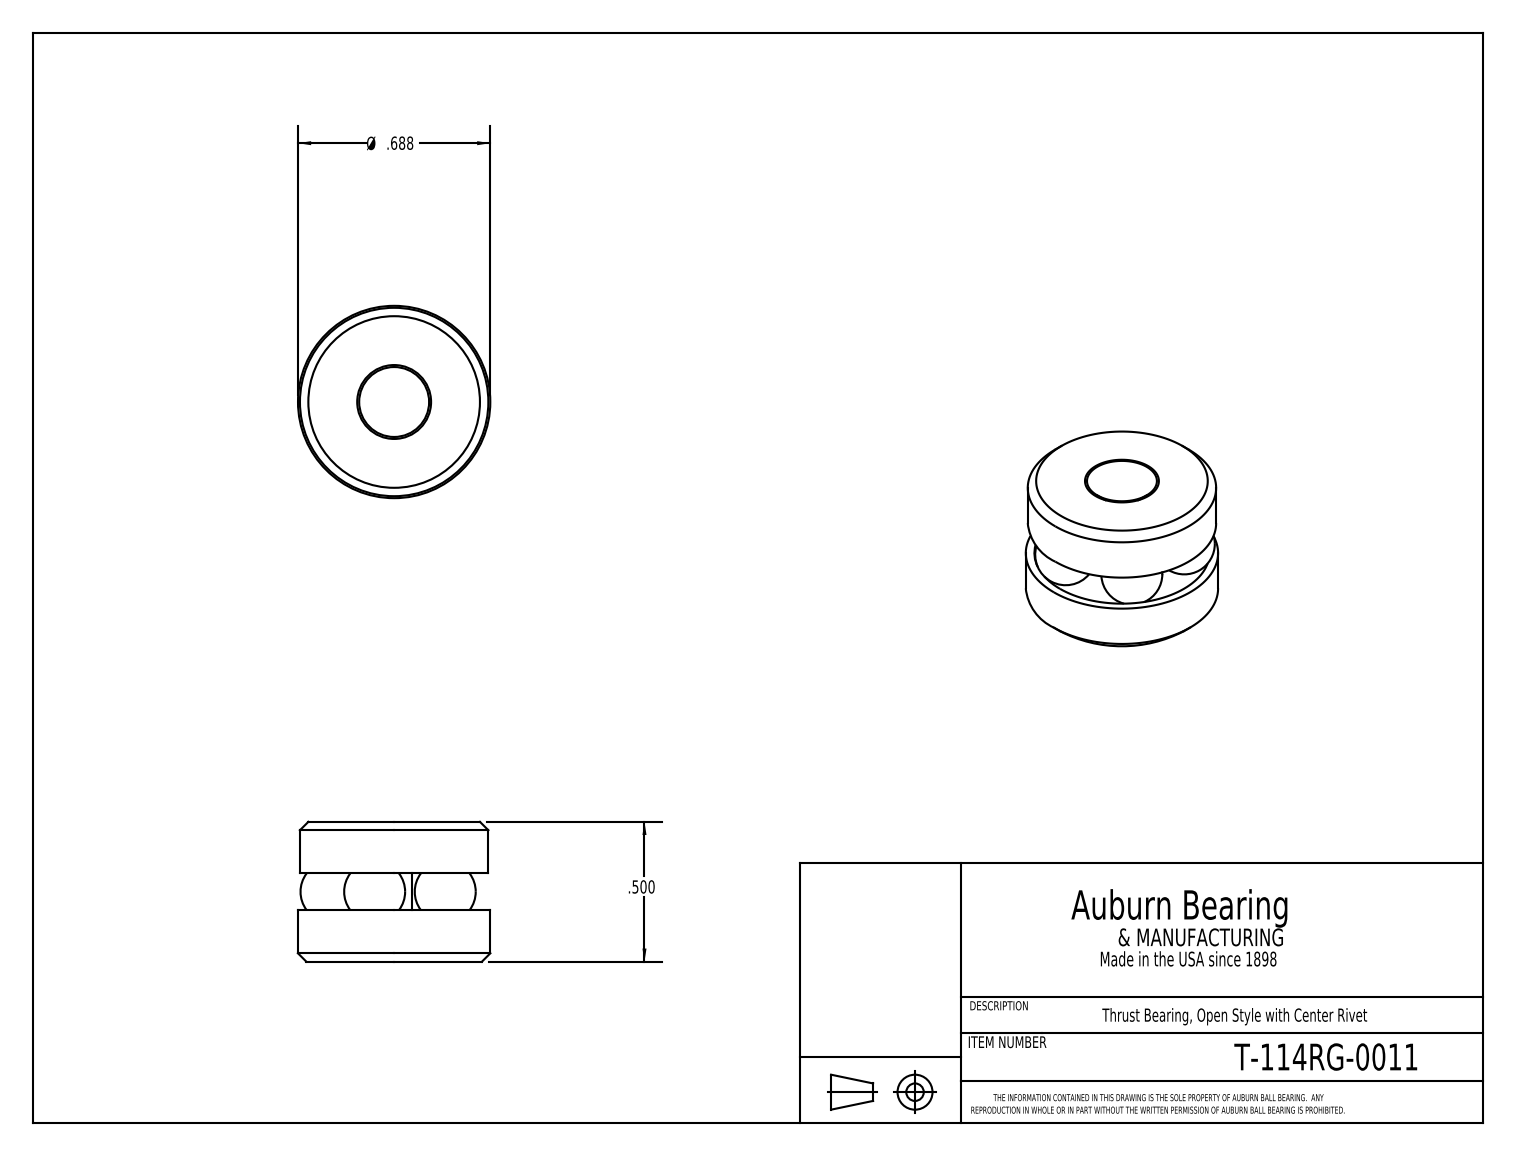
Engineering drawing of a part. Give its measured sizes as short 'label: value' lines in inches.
name: T-114RG_T-114RG-0011
written by: SolidWorks 2016 (CONFIG_CONTROL_DESIGN)
unit: in
bodies: 8 solids, 26 faces (8 planar, 5 cylindrical, 13 other)
size: 0.688 × 0.688 × 0.5
volume: 0.145 in³; area: 3.42 in²
holes: 1× ⌀0.135
bosses: 1× ⌀0.687, 1× ⌀0.673, 1× ⌀0.125
face distances: 0.5, 0.185, 0.315, 0.131
